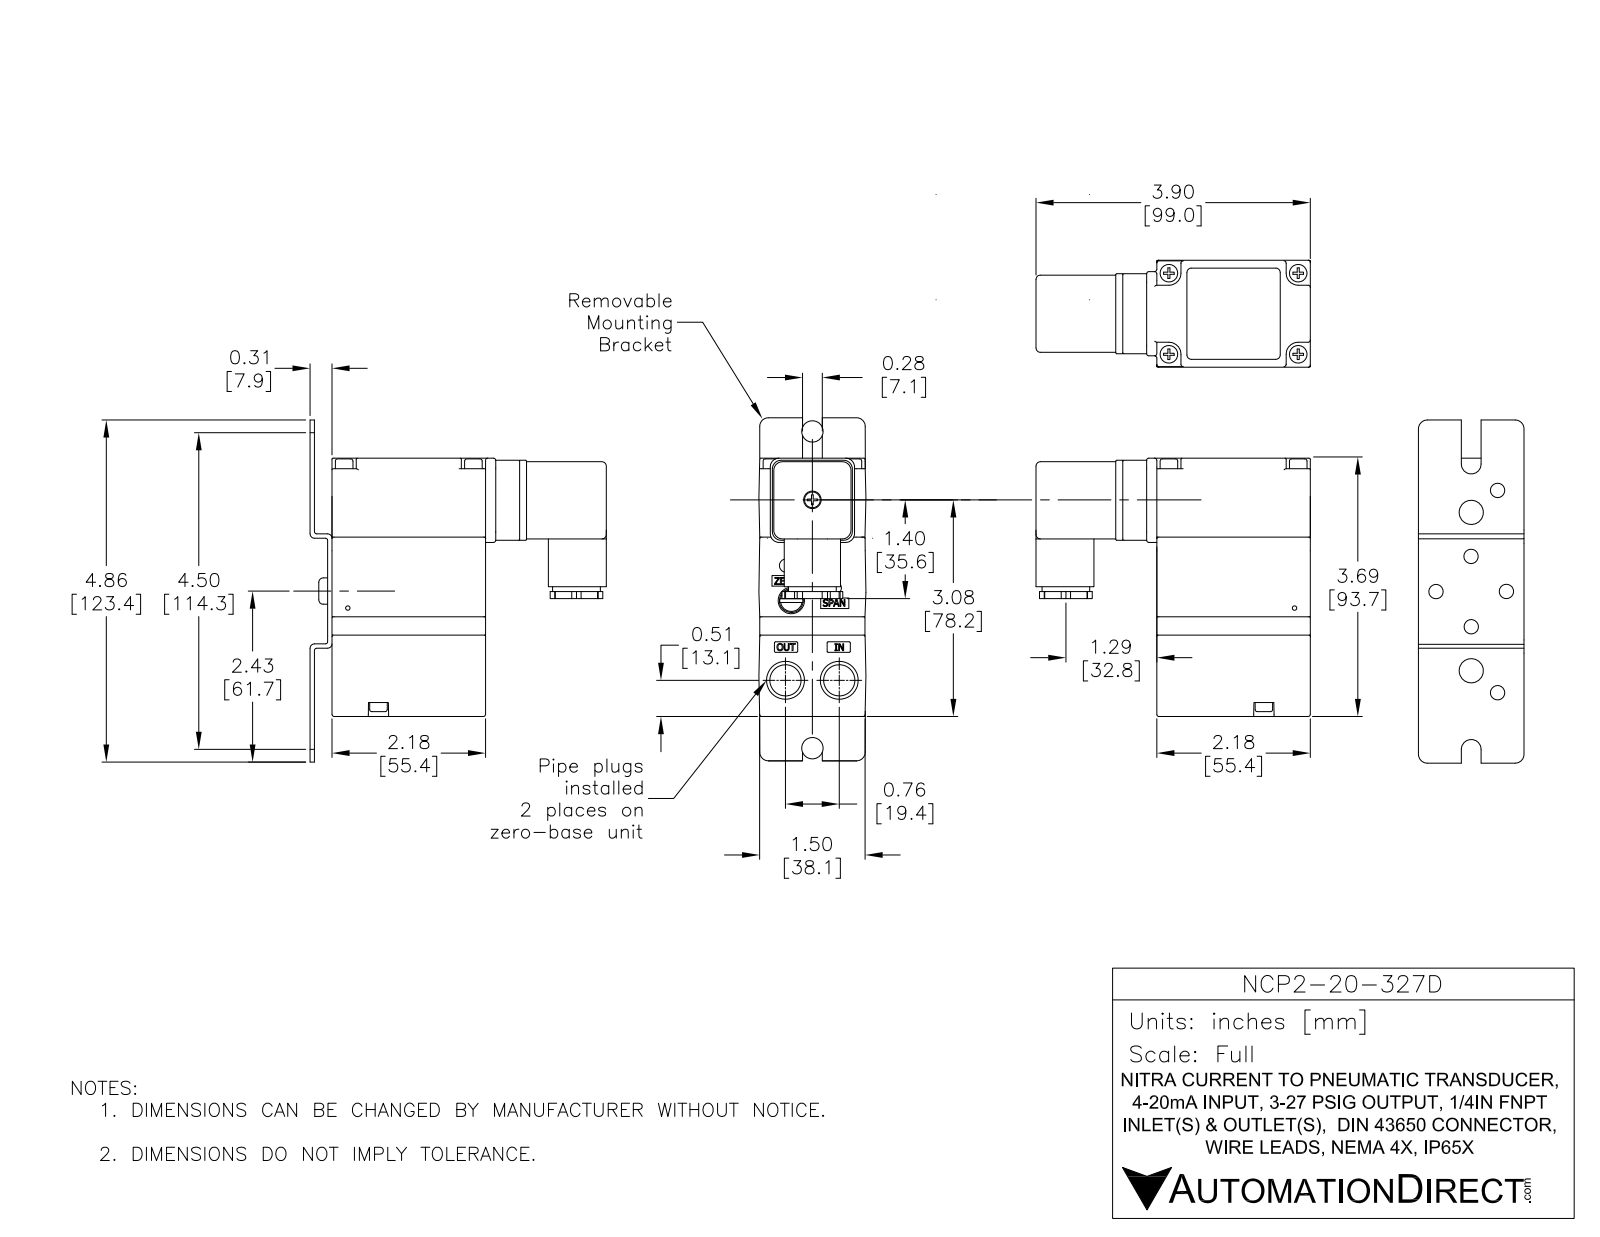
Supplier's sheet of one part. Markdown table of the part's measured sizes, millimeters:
| quantity | value |
| --- | --- |
| part name | NCP2-20-327D |
| STEP written by | SolidWorks 2016 (AUTOMOTIVE_DESIGN) |
| units | millimeters |
| bodies | 5 solids, 1129 faces (622 planar, 321 cylindrical, 186 other) |
| overall size | 123.83 × 107.43 × 38.77 |
| volume | 223 787 mm³ |
| surface area | 53 073 mm² |
| round holes (diameter × count) | 5.16 × 6, 3.37 × 3, 3.18 × 2, 3.3 × 2, 4.8 × 2, 8.73 × 2, 11.38 × 2, 1.59 × 1, 3.17 × 1, 6.35 × 1, 7.37 × 1, 11.43 × 1 |
| round bosses / shafts (diameter × count) | 6.6 × 4, 6.35 × 3, 7.49 × 2, 20.32 × 1, 18.32 × 1, 16.18 × 1, 11.43 × 1, 8.66 × 1 |
| partial cylindrical surfaces (radius × count) | 0.76 × 56, 3.17 × 20, 0.5 × 17, 0.4 × 12, 1.47 × 6, 1.59 × 6, 0.79 × 4, 1.25 × 4 |
| main face-to-face distances | 1.59, 6.85, 8.44, 55.55, 37.35, 38.74, 1.39, 6.74, 8.33, 1.69 |
| hole center spacings | 25.4, 33.68, 12.4, 17.74, 17.94, 18.41, 18.78, 21.29 |
